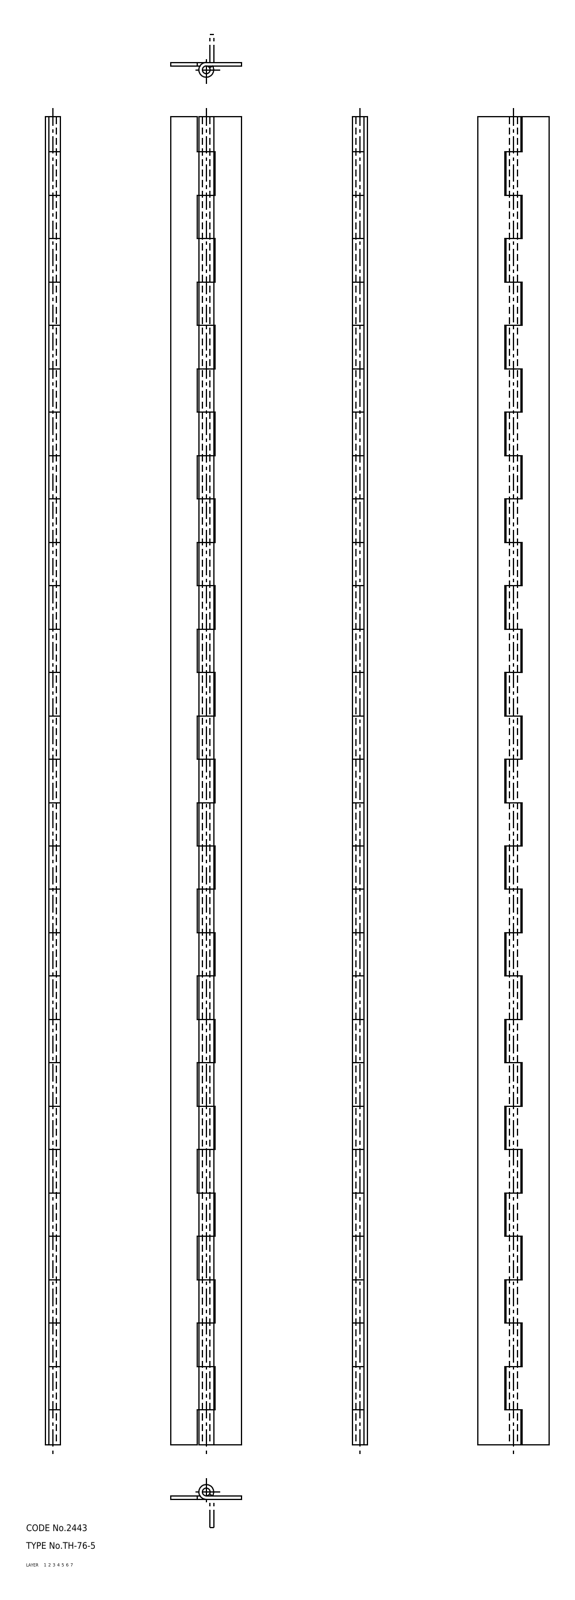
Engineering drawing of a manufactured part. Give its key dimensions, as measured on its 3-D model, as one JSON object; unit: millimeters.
{"part_name": "shaft; TH_76_5; hinge piece_A; hinge piece_B", "step_written_by": "SolidWorks 2015 (AUTOMOTIVE_DESIGN)", "units": "millimeters", "bodies": {"solids": 3, "faces": 198, "planar": 134, "cylindrical": 64, "other": 0}, "overall_size": [600, 32, 6.7], "volume_mm3": 45449, "surface_area_mm2": 61848, "round_holes": [[3.5, 1]], "round_bosses_or_shafts": [[6.7, 1]], "face_to_face_distances": [1.6, 32, 12, 20, 39.2, 78.4, 117.6, 156.8, 196, 8]}
